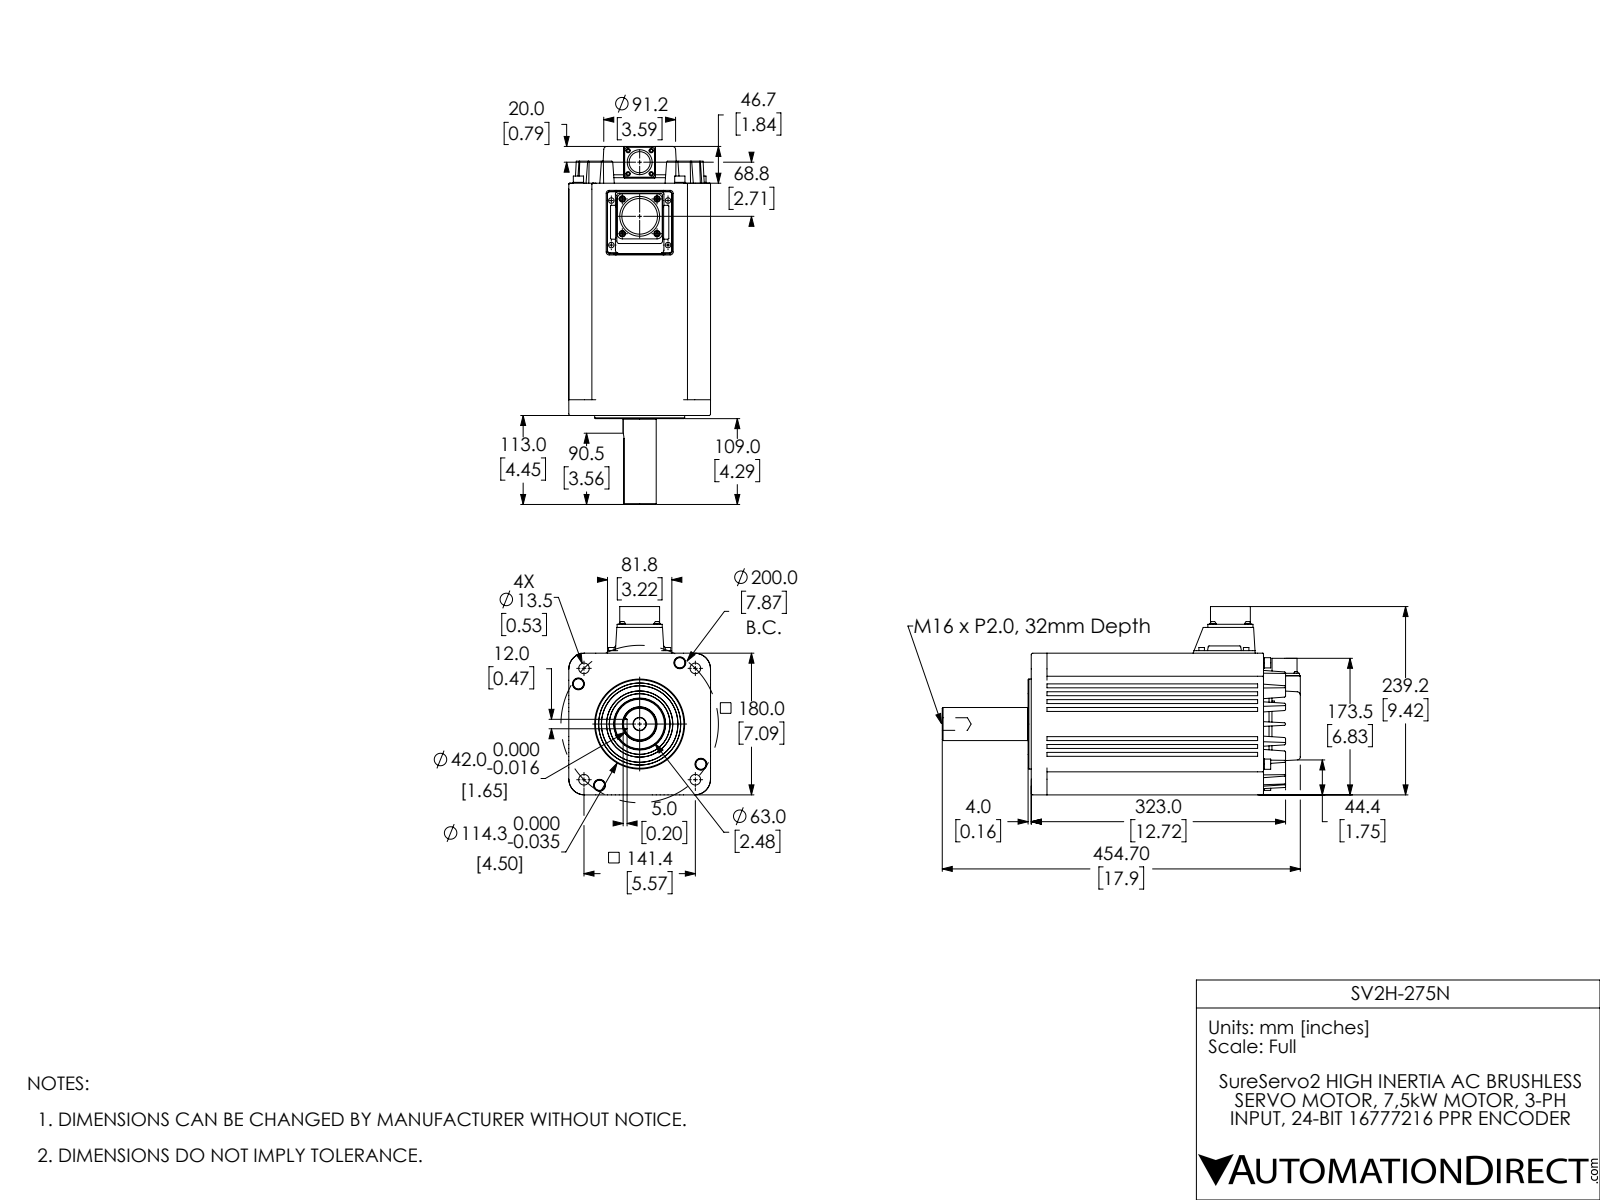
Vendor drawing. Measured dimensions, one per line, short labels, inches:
name: SV2H-275N
written by: SolidWorks 2017 (AUTOMOTIVE_DESIGN)
unit: in
bodies: 1 solid, 616 faces (319 planar, 216 cylindrical, 81 other)
size: 17.902 × 9.417 × 7.087
volume: 561 in³; area: 666.6 in²
holes: 4× ⌀0.531, 1× ⌀0.63, 1× ⌀1.058, 1× ⌀1.783, 1× ⌀2.48
bosses: 8× ⌀0.315, 4× ⌀0.528, 4× ⌀0.512, 4× ⌀0.276, 3× ⌀0.217, 1× ⌀4.567, 1× ⌀4.5, 1× ⌀1.992
rounds: 16× R0.039, 16× R0.064, 16× R0.197, 8× R0.118, 8× R0.15, 8× R0.157, 4× R0.02, 4× R0.079
face distances: 0.197, 0.394, 7.087, 1.154, 0.591, 5.933, 3.031, 3.228, 2.835, 0.787
hole spacings: 3.937, 5.568, 7.874, 2.707
